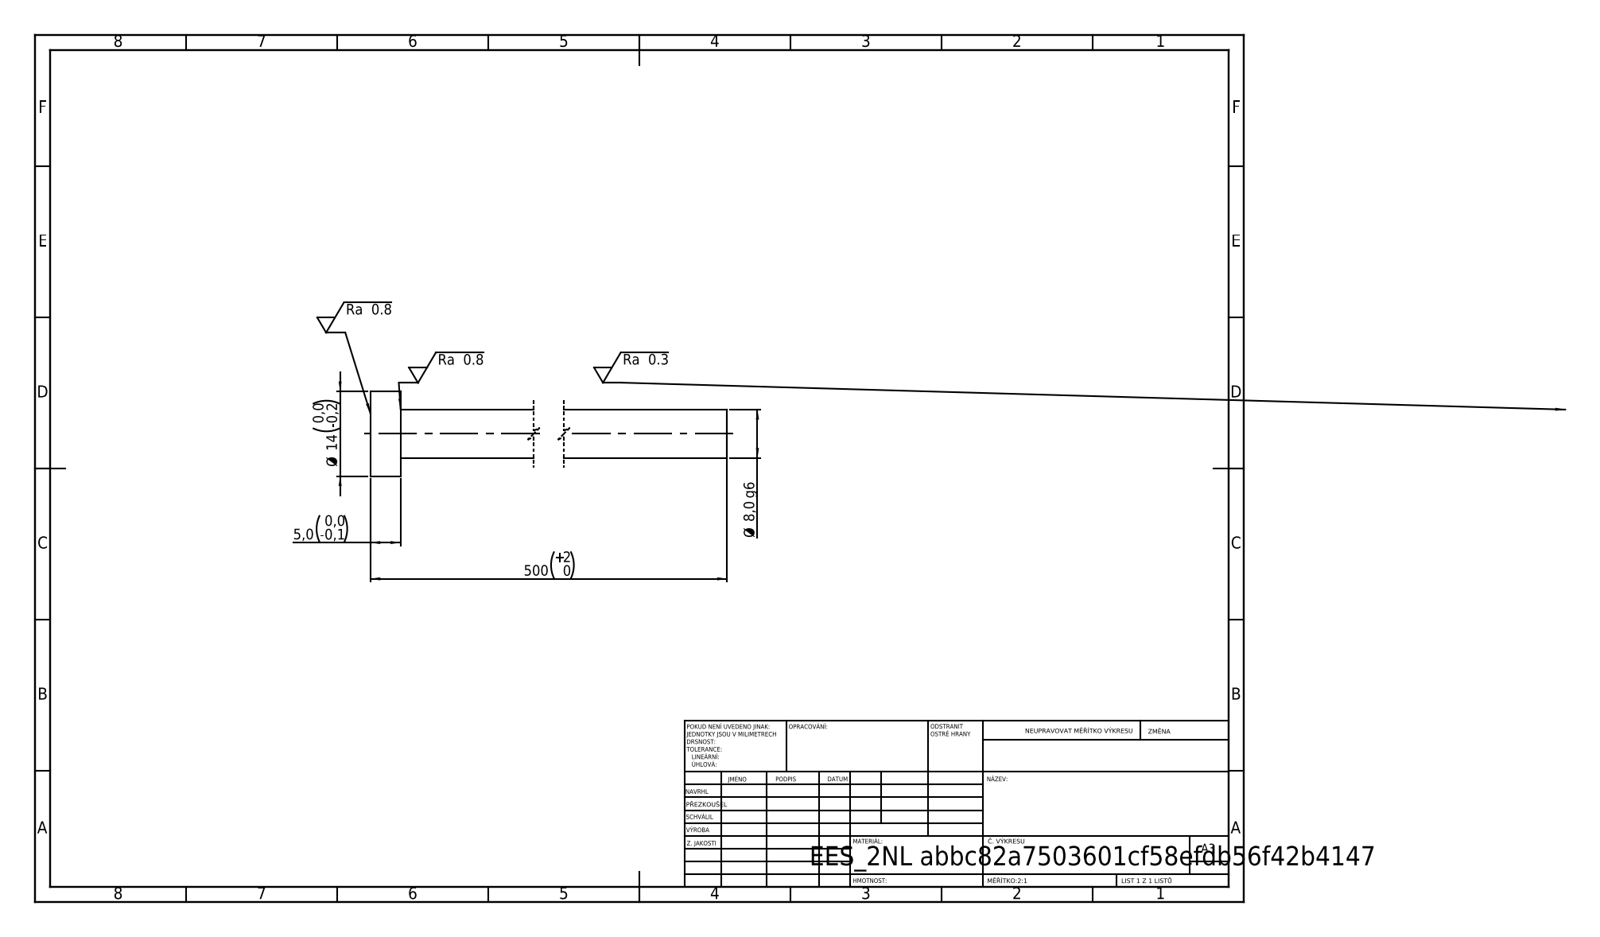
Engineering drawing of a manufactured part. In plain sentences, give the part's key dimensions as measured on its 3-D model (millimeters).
Its 3-D file was written by "SolidWorks 2019 (CONFIG_CONTROL_DESIGN)". It is 1 solid with 7 faces: 3 planar, 4 cylindrical and 0 other. Overall it measures 500 by 14 by 14 millimeters. Its volume is 25 651 cubic millimeters and its surface area 12 968 square millimeters. Round bosses or shafts: 1 of diameter 14, 1 of diameter 8. The main face-to-face distances are 5, 500, 495.
